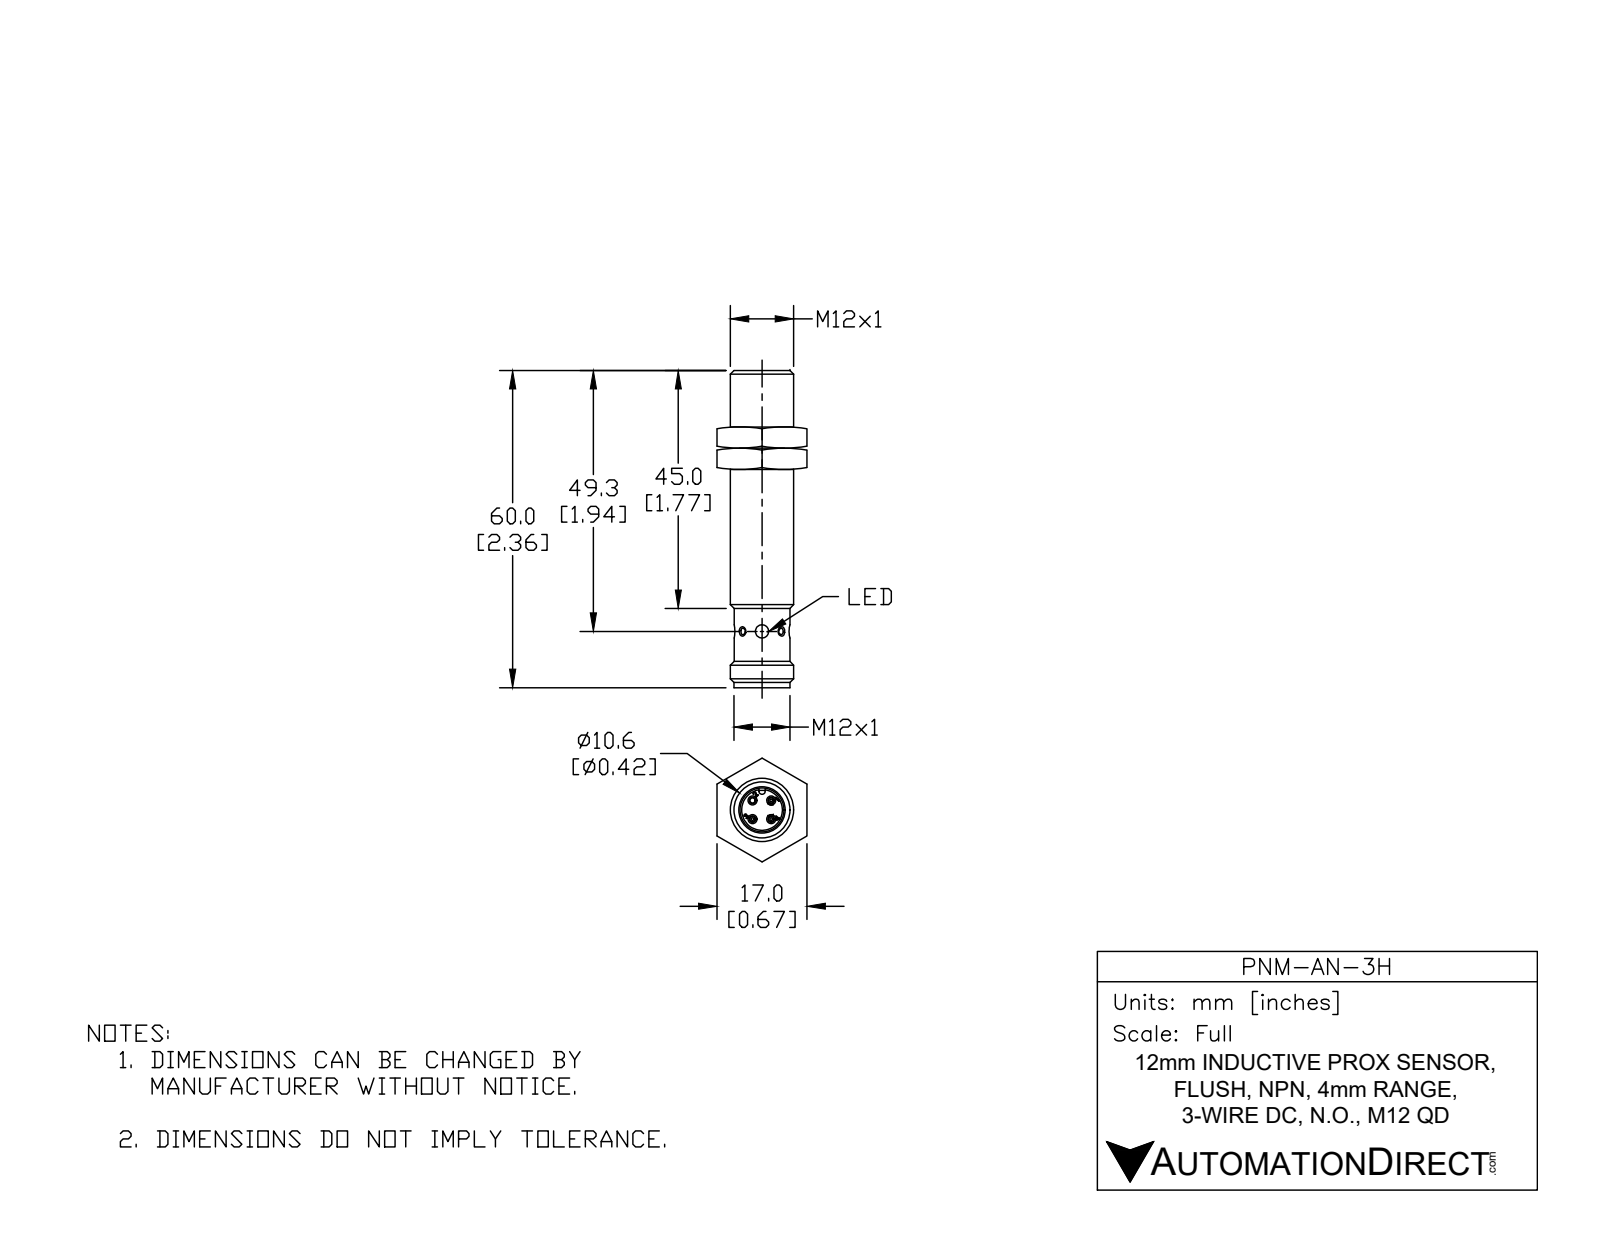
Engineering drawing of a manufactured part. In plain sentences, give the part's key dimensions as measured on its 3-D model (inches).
The part is named "PNM-AN-3H". Its 3-D file was written by "SolidWorks 2017 (AUTOMOTIVE_DESIGN)". It is 1 solid with 479 faces: 119 planar, 134 cylindrical and 226 other. Overall it measures 2.362 by 0.472 by 0.472 inches. Its volume is 0.35 cubic inches and its surface area 10.25 square inches. Round holes: 3 of diameter 0.043, 2 of diameter 0.04, 2 of diameter 0.098, 1 of diameter 0.038, 1 of diameter 0.04, 1 of diameter 0.327, 1 of diameter 0.394, 1 of diameter 0.401. Round bosses or shafts: 9 of diameter 0.039, 1 of diameter 0.472, 1 of diameter 0.417, 1 of diameter 0.415, 1 of diameter 0.4, 1 of diameter 0.392, 1 of diameter 0.39, 1 of diameter 0.376. Partial cylindrical surfaces (rounded edges, fillets, slot ends): 36 of radius 0.004, 1 of radius 0.024, 1 of radius 0.031, 1 of radius 0.161. The main face-to-face distances are 0.039, 1.87, 1.831, 0.018, 0.022, 1.852, 2.323, 0.142, 2.012, 1.994. The hole center spacings are 0.098, 0.139, 0.197.
